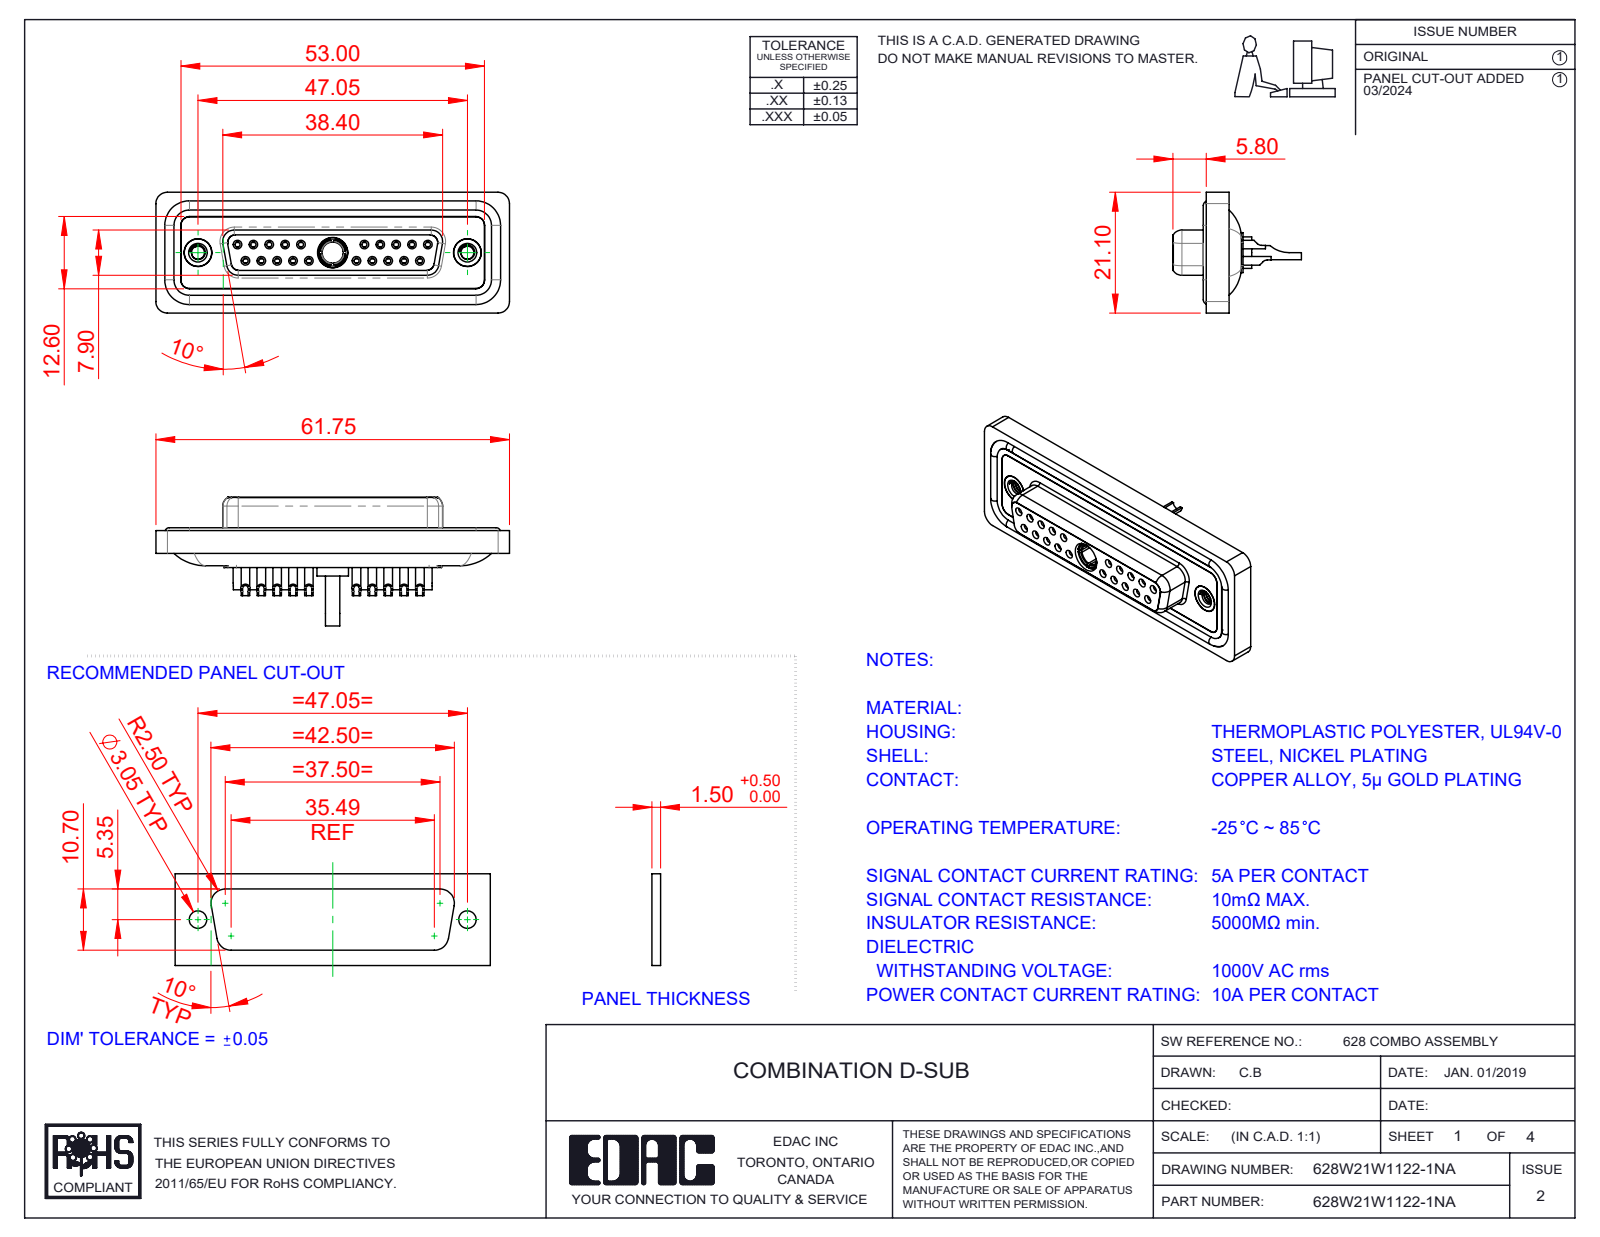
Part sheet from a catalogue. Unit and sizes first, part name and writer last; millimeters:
Units: millimetres
Overall size (bounding box): 61.75 × 22.45 × 21.1
Round holes (diameter × count): ⌀0.9 ×20, ⌀1 ×20, ⌀1.1 ×20, ⌀1.5 ×20, ⌀2 ×20, ⌀1.6 ×10, ⌀1.7 ×10, ⌀4.85 ×3, ⌀2.26 ×2, ⌀4 ×2, ⌀4.05 ×2, ⌀5 ×2
Round bosses / shafts (diameter × count): ⌀2.2 ×20, ⌀1.6 ×14, ⌀4.95 ×2, ⌀4.8 ×2, ⌀5.5 ×1, ⌀5.2 ×1, ⌀4.96 ×1, ⌀4.75 ×1
Partial cylindrical surfaces — rounded edges, fillets, slot ends (radius × count): R1.5 ×22, R2 ×18, R1.35 ×8, R1.6 ×8, R1 ×6, R0.25 ×4, R0.5 ×4, R0.6 ×4
Main face-to-face distances: 0.4, 1.8, 7.45, 5.65, 6.6, 0.5, 1.6, 7.05, 2.9, 1.1
Hole centre spacings: 3.16, 2.77, 5.54, 5.03, 8.31, 7.48, 16.62, 19.39
Volume: 8 414 mm³ · Surface area: 14 257 mm²
Bodies: 29 solids, 1563 faces (476 planar, 636 cylindrical, 451 other)
Part name (STEP PRODUCT): 628Combo Waterproof Housing_25 Contacts; 628Combo Shell Rear_25 Contacts; 628Combo Housing_21W1; Power Socket_10A SC (+5 more)
STEP written by: SolidWorks 2023 (CONFIG_CONTROL_DESIGN)
